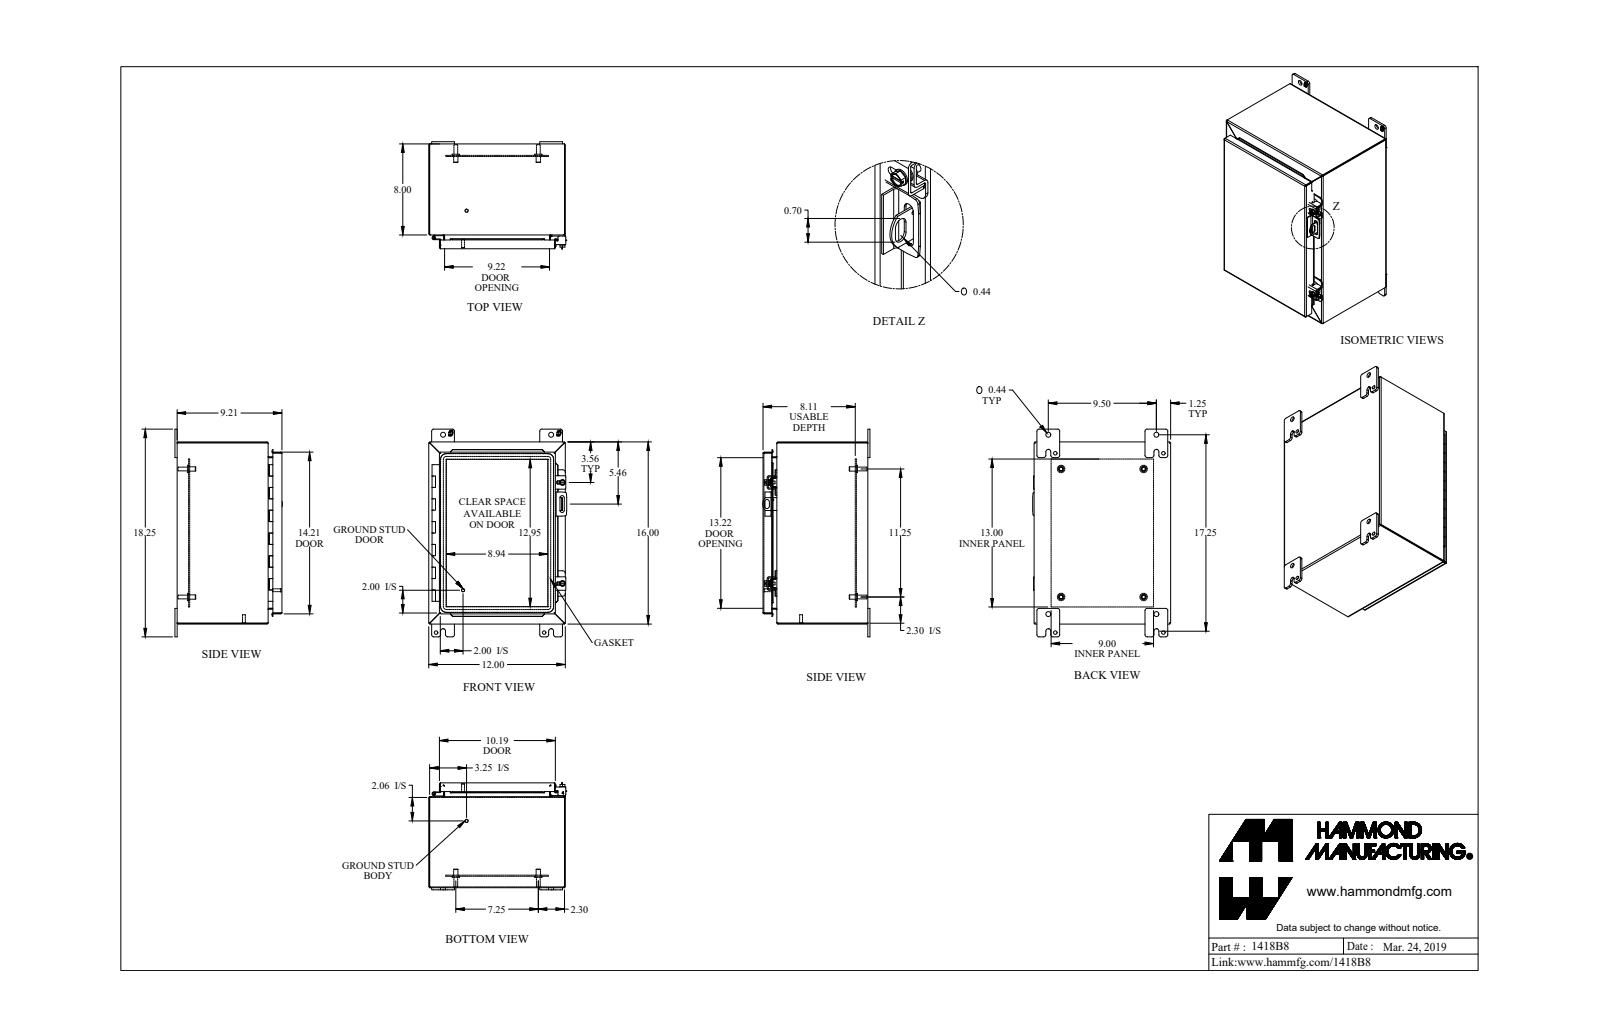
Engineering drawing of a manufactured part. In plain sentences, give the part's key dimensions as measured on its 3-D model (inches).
The part is named "1418B8". Its 3-D file was written by "SolidWorks 2019 (AUTOMOTIVE_DESIGN)". It is 38 solids with 954 faces: 657 planar, 243 cylindrical and 54 other. Overall it measures 18.25 by 12.125 by 9.437 inches. Its volume is 92.56 cubic inches and its surface area 2 411 square inches. Round holes: 4 of diameter 0.313, 4 of diameter 0.437, 4 of diameter 0.5, 2 of diameter 0.213, 2 of diameter 0.265, 2 of diameter 0.307, 2 of diameter 0.375, 2 of diameter 0.445, 1 of diameter 0.125, 1 of diameter 0.187. Round bosses or shafts: 4 of diameter 0.65, 4 of diameter 0.375, 4 of diameter 0.33, 2 of diameter 1, 2 of diameter 0.5, 2 of diameter 0.39, 2 of diameter 0.281, 2 of diameter 0.25. Partial cylindrical surfaces (rounded edges, fillets, slot ends): 26 of radius 0.188, 20 of radius 0.036, 20 of radius 0.108, 13 of radius 0.048, 13 of radius 0.143, 8 of radius 0.007, 8 of radius 0.045, 8 of radius 0.079. The main face-to-face distances are 0.072, 9.113, 11.928, 9.041, 15.928, 0.937, 9.185, 1.009, 1.185, 7.928. The hole center spacings are 9.5, 18.393, 7.25, 8.508, 10.285, 12.8, 13.384, 1.735.
